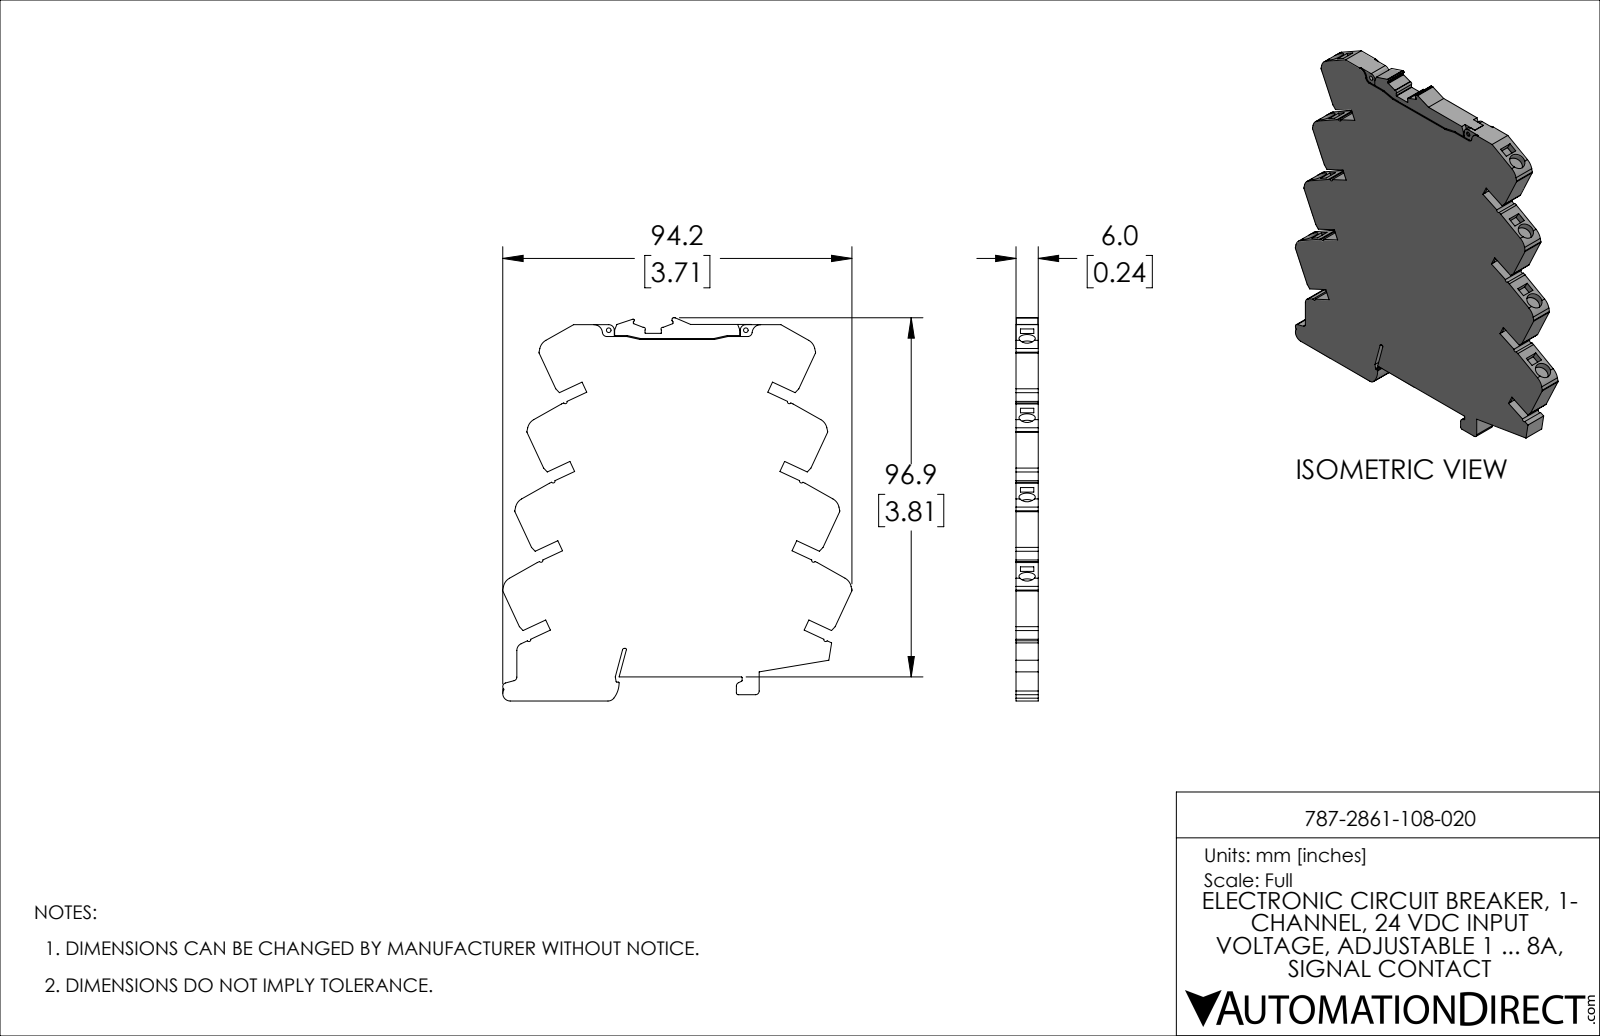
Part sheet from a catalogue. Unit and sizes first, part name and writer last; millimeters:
Units: millimetres
Overall size (bounding box): 103.36 × 94.26 × 6
Round holes (diameter × count): ⌀4.4 ×8, ⌀1.25 ×2
Partial cylindrical surfaces — rounded edges, fillets, slot ends (radius × count): R0.5 ×12, R0.2 ×11, R0.4 ×8, R3.35 ×8, R1 ×4, R0.3 ×3, R2 ×3, R0.45 ×2
Main face-to-face distances: 6, 17.99, 17.02, 12.01, 5.9, 12, 3, 24.01, 35.98, 6.5
Hole centre spacings: 13.35, 13.34, 26.7, 26.69, 26.71, 37, 40.04, 40.05
Volume: 43 932 mm³ · Surface area: 19 262 mm²
Bodies: 1 solid, 294 faces (219 planar, 75 cylindrical, 0 other)
Part name (STEP PRODUCT): 787-2861/108-020
STEP written by: PARTsolutions (CONFIG_CONTROL_DESIGN)
